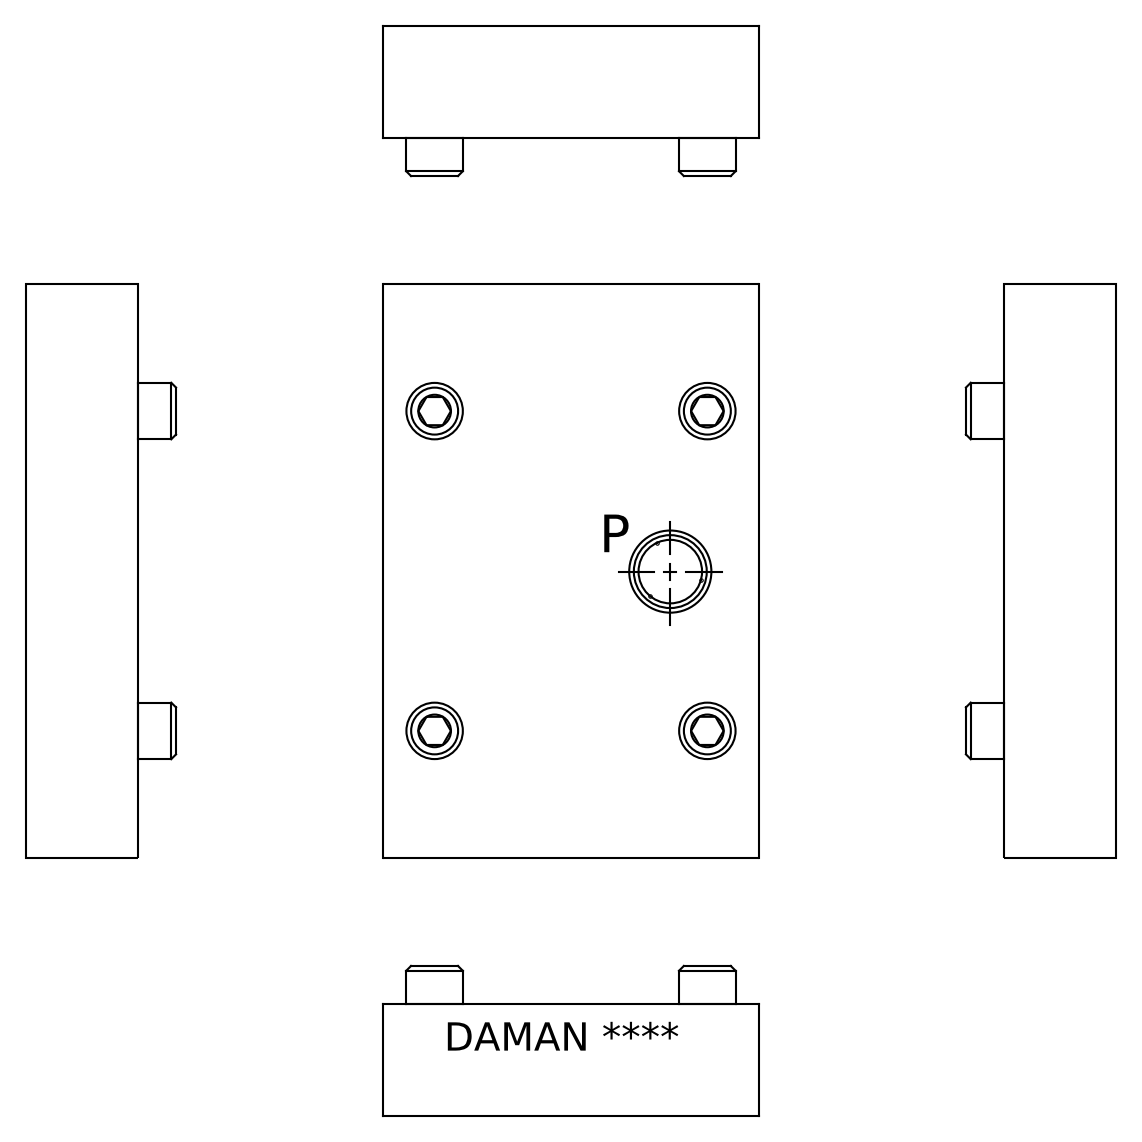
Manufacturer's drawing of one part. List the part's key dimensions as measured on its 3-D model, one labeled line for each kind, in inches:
Part name (STEP PRODUCT): D05HCPPG
STEP written by: Autodesk Inventor 2020 (AUTOMOTIVE_DESIGN)
Units: inches
Bodies: 1 solid, 355 faces (245 planar, 15 cylindrical, 95 other)
Overall size (bounding box): 3.812 × 2.5 × 0.75
Volume: 6.717 in³ · Surface area: 32.34 in²
Round holes (diameter × count): ⌀0.625 ×6, ⌀0.281 ×4, ⌀0.422 ×1, ⌀0.438 ×1, ⌀0.546 ×1
Partial cylindrical surfaces — rounded edges, fillets, slot ends (radius × count): R0.187 ×1, R0.313 ×1
Main face-to-face distances: 0.75, 2.5, 0.71, 0.04, 3.812, 0.052, 0.698, 3.802, 0.301, 0.261
Hole centre spacings: 1.287, 1.694, 2.477, 2.793, 0.448, 0.537, 0.546, 0.546
